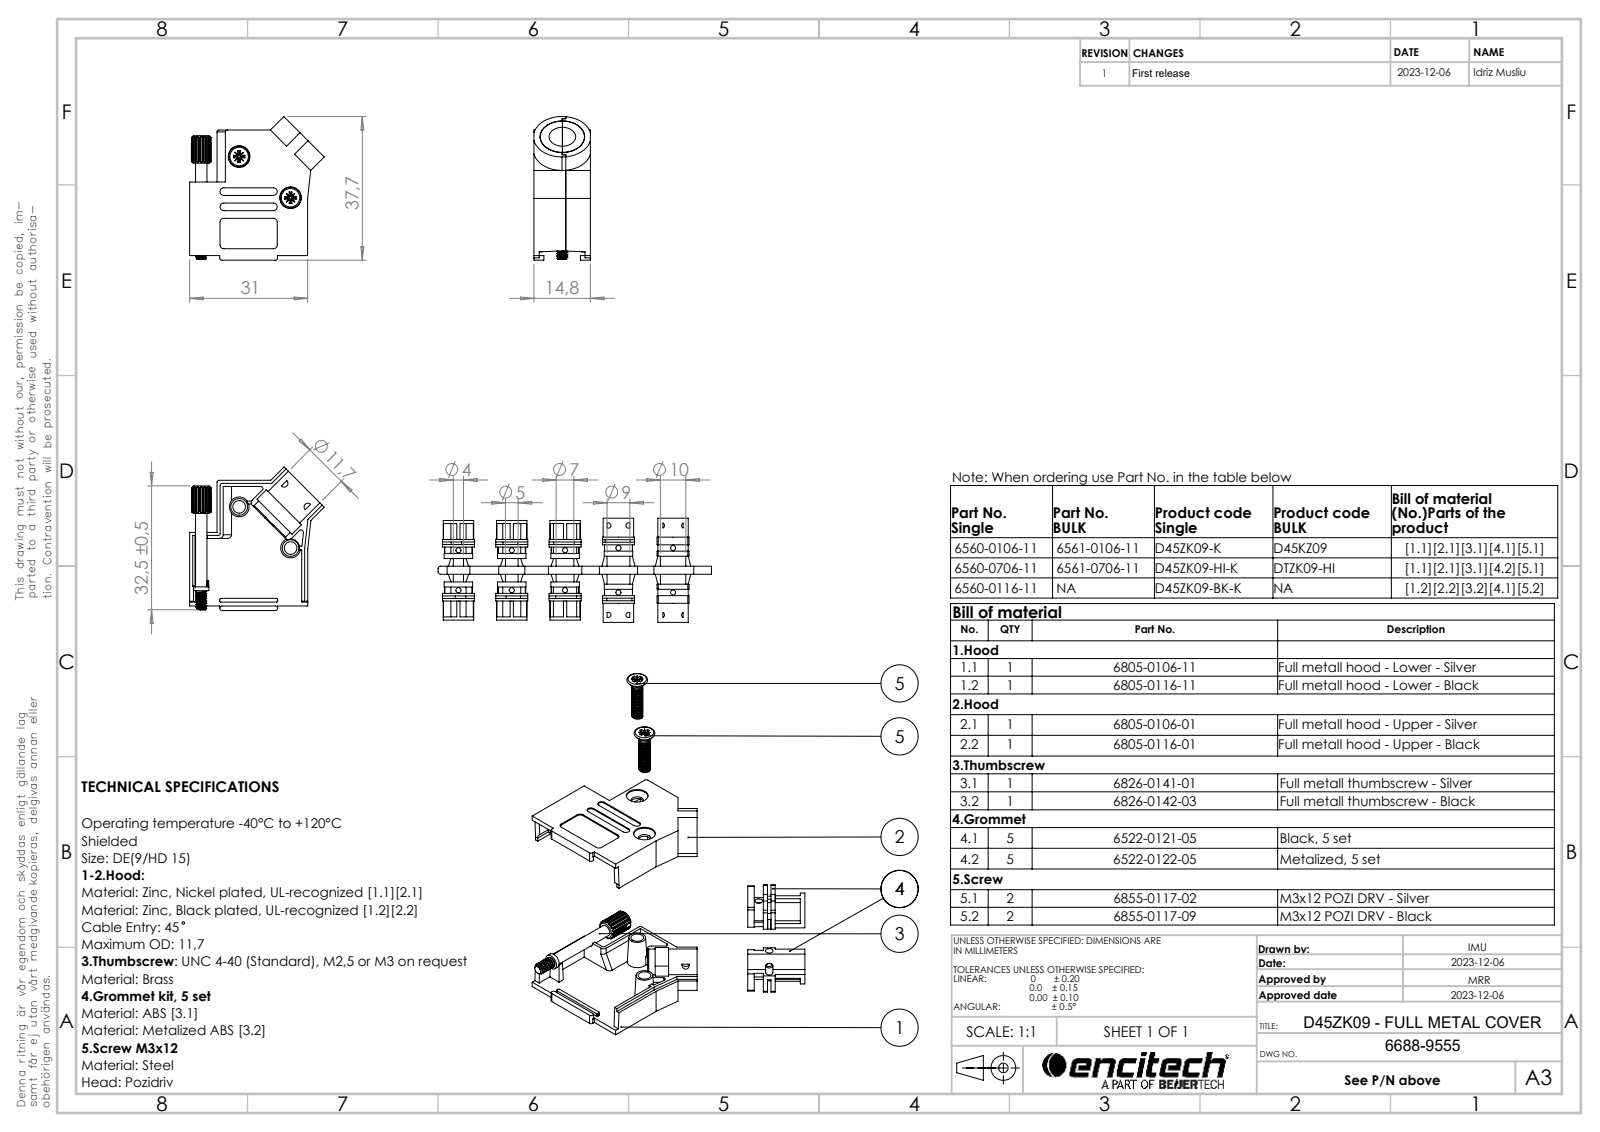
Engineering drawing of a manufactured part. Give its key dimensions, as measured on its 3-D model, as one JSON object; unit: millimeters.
{"part_name": "6522-0121-05 (7mm); 6805-0106-01; 6805-0106-11; 6826-0141-01 (+2 more)", "step_written_by": "SolidWorks 2021 (AUTOMOTIVE_DESIGN)", "units": "millimeters", "bodies": {"solids": 7, "faces": 681, "planar": 371, "cylindrical": 251, "other": 59}, "overall_size": [37.7, 35.35, 14.8], "volume_mm3": 5963, "surface_area_mm2": 9668, "round_holes": [[2, 3], [3.3, 2], [5.7, 2], [7, 1]], "round_bosses_or_shafts": [[2.9, 2], [1.9, 2], [11.6, 1], [9.2, 1], [4, 1], [3, 1], [2.85, 1]], "partial_cylinders_radius": [[1, 20], [0.5, 13], [0.1, 8], [0.3, 4], [5.91, 4], [0.6, 2], [1.65, 2], [5.64, 2]], "face_to_face_distances": [1.4, 14.8, 13.4, 13.45, 12.05, 1.35, 1.6, 14.5, 29.4, 0.8], "hole_center_spacings": [5.71, 5.87, 7.22, 8.97, 9.13, 10, 14.51, 14.82]}
